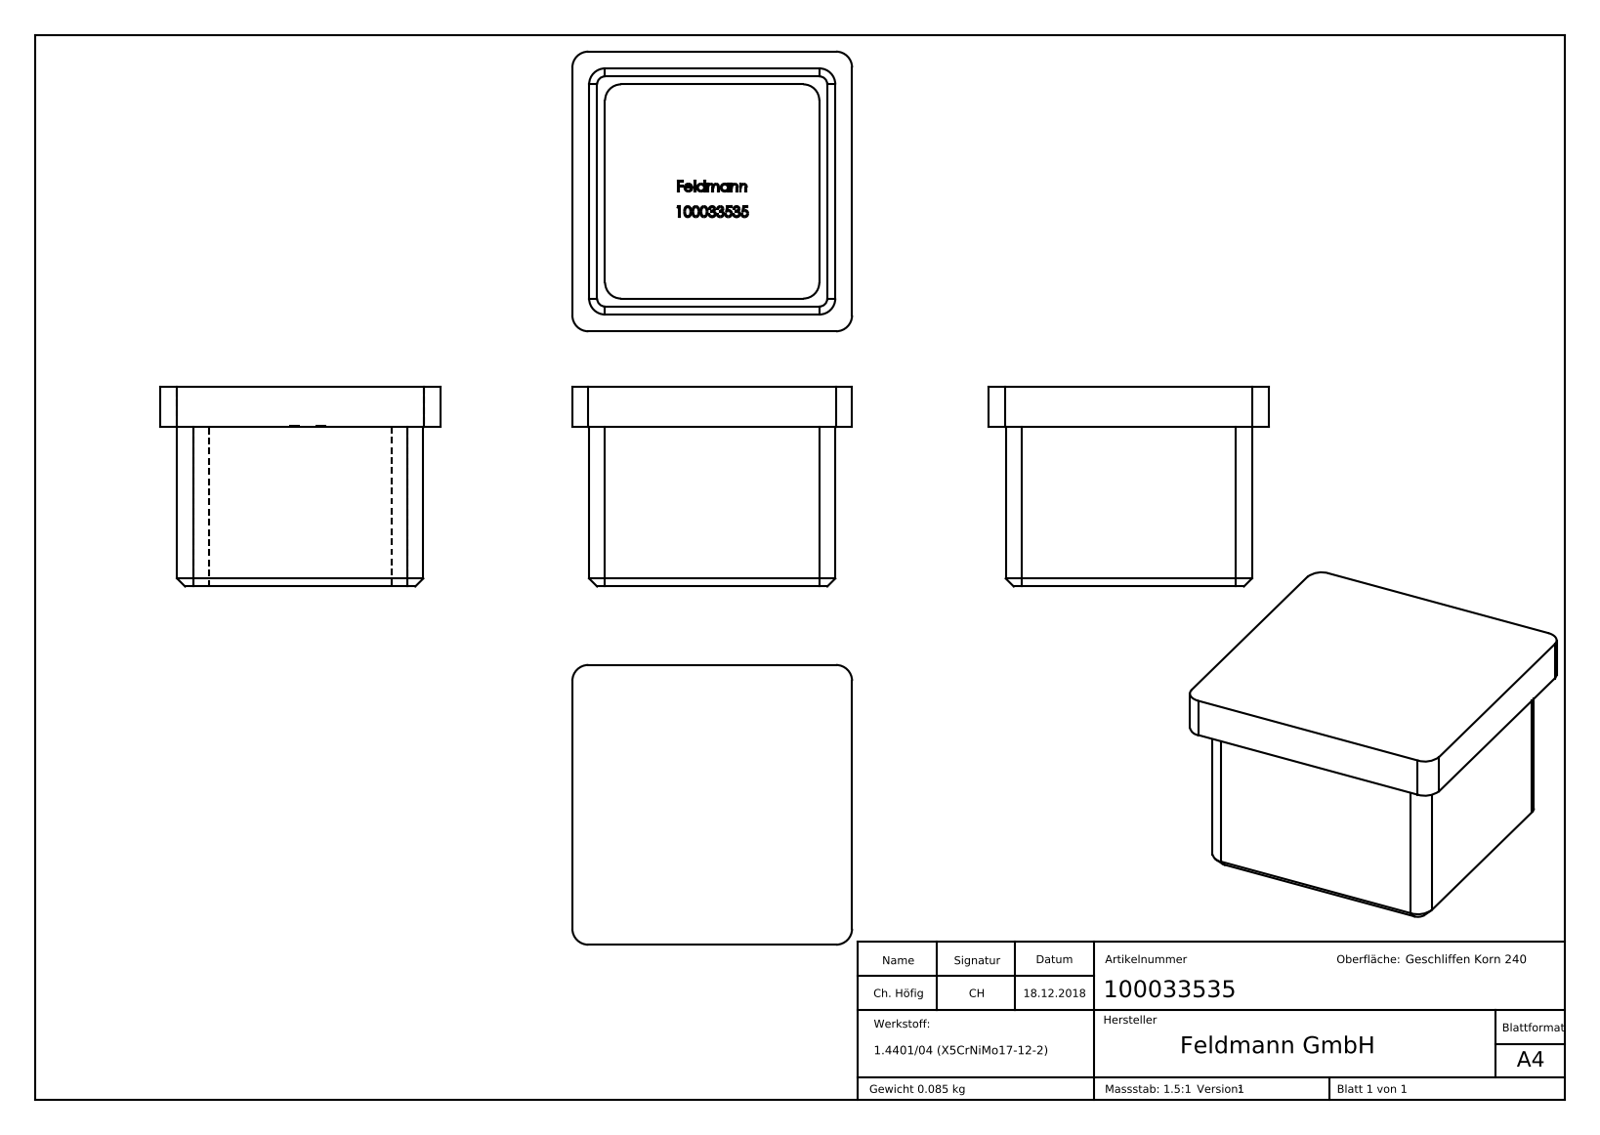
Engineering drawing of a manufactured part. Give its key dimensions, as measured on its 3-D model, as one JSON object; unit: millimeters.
{"part_name": "100033535", "step_written_by": "SolidWorks 2015 (CONFIG_CONTROL_DESIGN)", "units": "millimeters", "bodies": {"solids": 1, "faces": 273, "planar": 124, "cylindrical": 12, "other": 137}, "overall_size": [35, 35, 25], "volume_mm3": 10656, "surface_area_mm2": 7535, "partial_cylinders_radius": [[2, 12]], "face_to_face_distances": [2, 28.8, 30.8, 5, 26.8, 2.1, 4.1, 30.9, 32.9, 35]}
